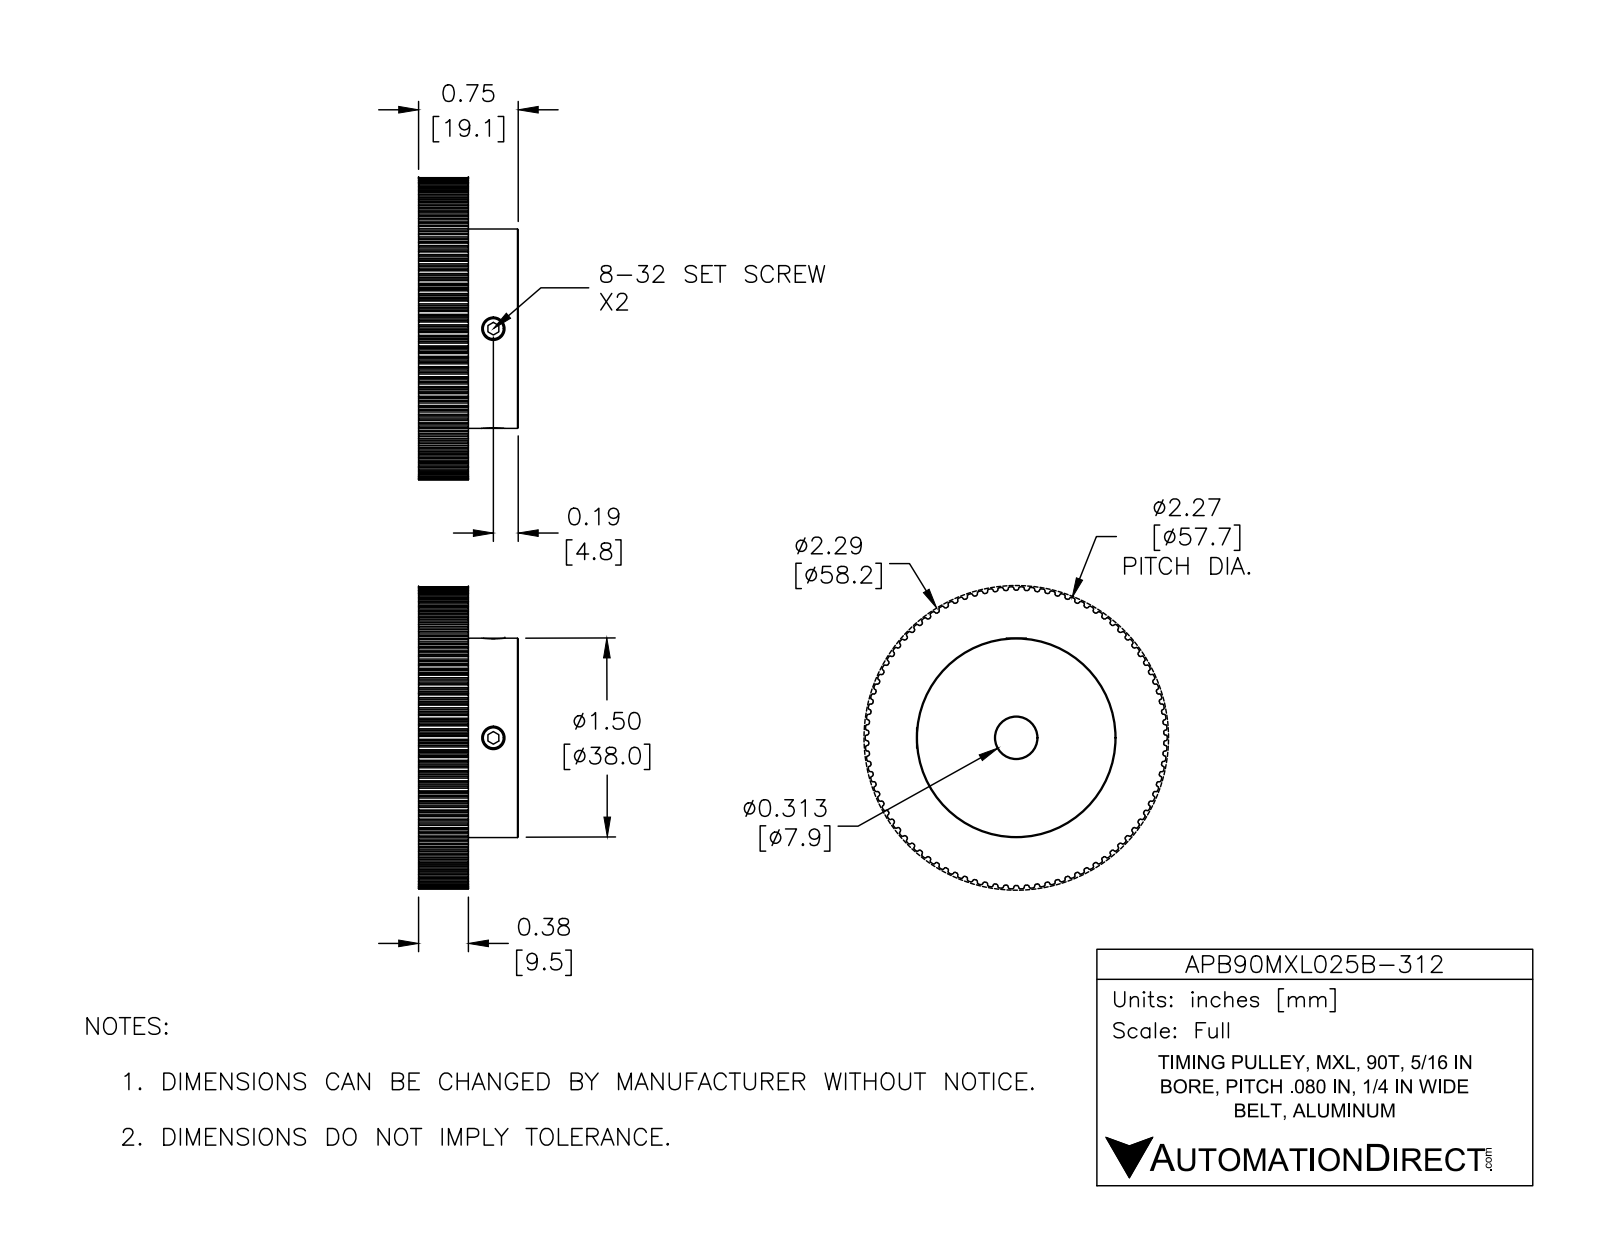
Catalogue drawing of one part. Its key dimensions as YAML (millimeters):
part_name: "APB90MXL025B-312"
step_written_by: "SolidWorks 2016 (AUTOMOTIVE_DESIGN)"
units: millimeters
bodies: {solids: 3, faces: 836, planar: 291, cylindrical: 531, other: 14}
overall_size: [57.7, 57.7, 19.1]
volume: 33990
surface_area: 9413
round_holes:
  - {diameter: 4.2, count: 2}
  - {diameter: 8, count: 1}
round_bosses_or_shafts:
  - {diameter: 4.1, count: 2}
  - {diameter: 38.1, count: 1}
partial_cylinders:
  - {radius: 0.2, count: 180}
  - {radius: 0.3, count: 180}
  - {radius: 28.9, count: 1}
face_to_face_distances: [9.5, 19.1, 9.5, 18.7, 18.6, 18.7, 18.7, 56.4, 18.6, 56.4]
